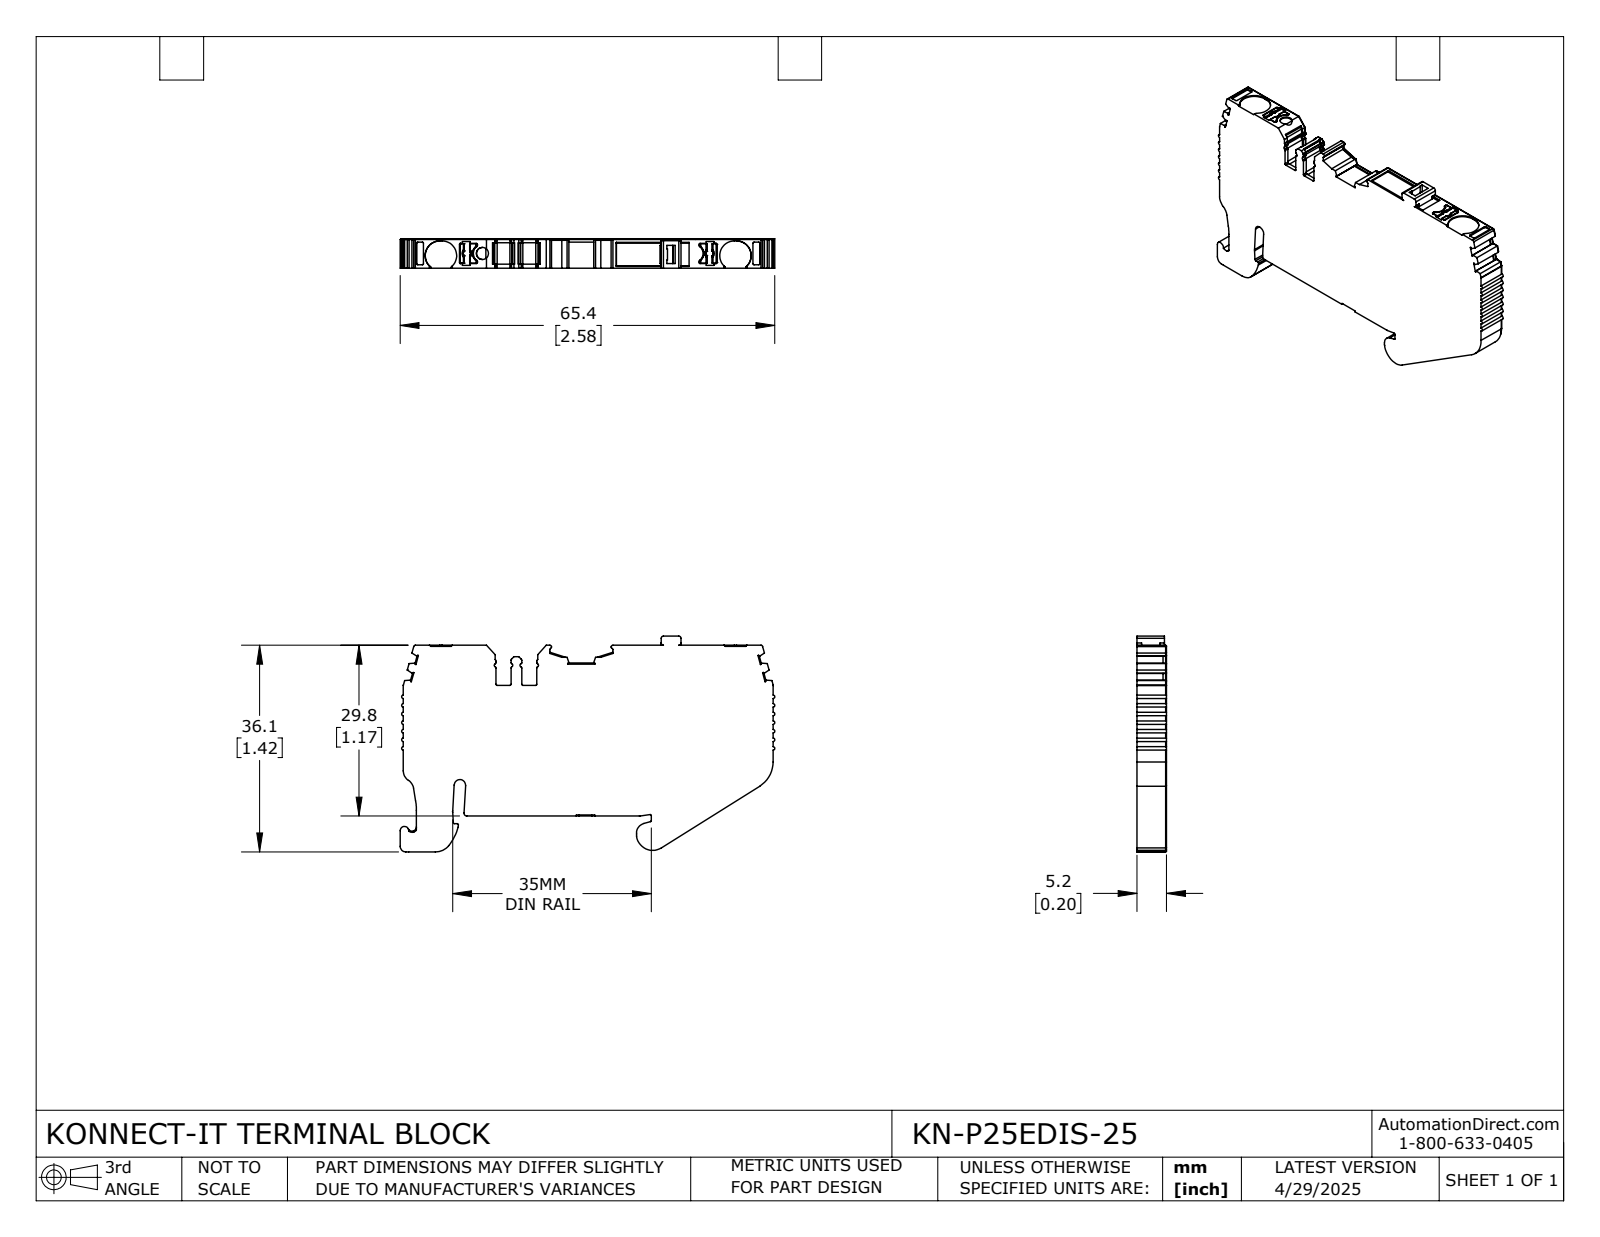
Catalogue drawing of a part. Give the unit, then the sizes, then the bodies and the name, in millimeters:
Units: millimetres
Overall size (bounding box): 65.42 × 37.67 × 5.15
Round holes (diameter × count): ⌀2.1 ×1
Partial cylindrical surfaces — rounded edges, fillets, slot ends (radius × count): R0.2 ×54, R0.3 ×39, R0.5 ×18, R0.1 ×17, R0.4 ×13, R0.15 ×8, R1 ×4, R2.55 ×4
Main face-to-face distances: 5.15, 29.61, 29.81, 64.58, 4.5, 5, 2, 6.26, 35.87, 36.07
Volume: 9 594 mm³ · Surface area: 5 183 mm²
Bodies: 1 solid, 618 faces (346 planar, 237 cylindrical, 35 other)
Part name (STEP PRODUCT): KN-P25EDIS-25
STEP written by: SolidWorks 2024 (CONFIG_CONTROL_DESIGN)
